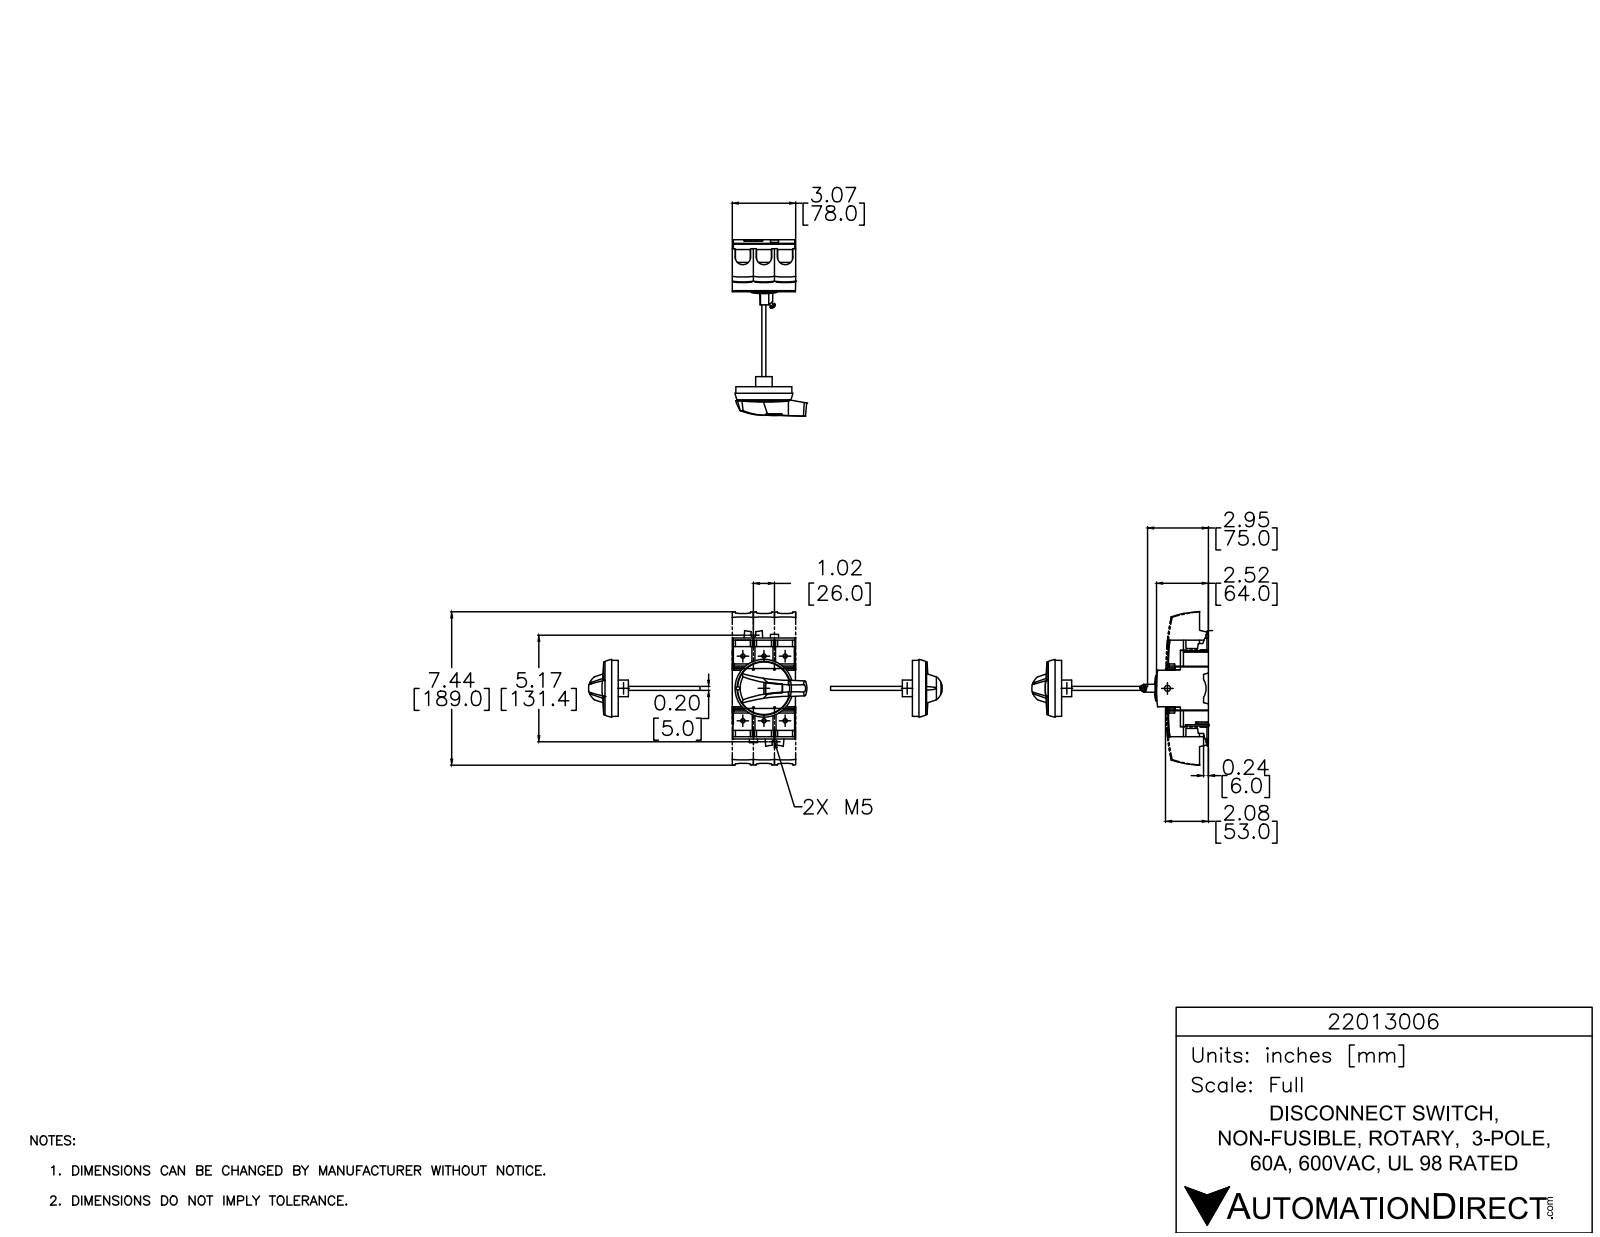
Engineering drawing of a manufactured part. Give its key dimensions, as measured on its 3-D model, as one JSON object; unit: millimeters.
{"part_name": "22013006", "step_written_by": "SolidWorks 2015 (AUTOMOTIVE_DESIGN)", "units": "millimeters", "bodies": {"solids": 1, "faces": 274, "planar": 210, "cylindrical": 45, "other": 19}, "overall_size": [142.7, 78.8, 64], "volume_mm3": 457500, "surface_area_mm2": 53740, "round_holes": [[5.2, 6], [7.2, 1], [9.3, 1], [32, 1]], "round_bosses_or_shafts": [[20.2, 1]], "partial_cylinders_radius": [[90, 3], [92.6, 3], [2.9, 2], [42.5, 2]], "face_to_face_distances": [77.8, 26, 7.9, 111, 1.1, 76.7, 2.5, 28.5, 46.9, 20.9], "hole_center_spacings": [26, 83.7, 79.6, 47.5, 47.5, 52, 95, 39.8]}
